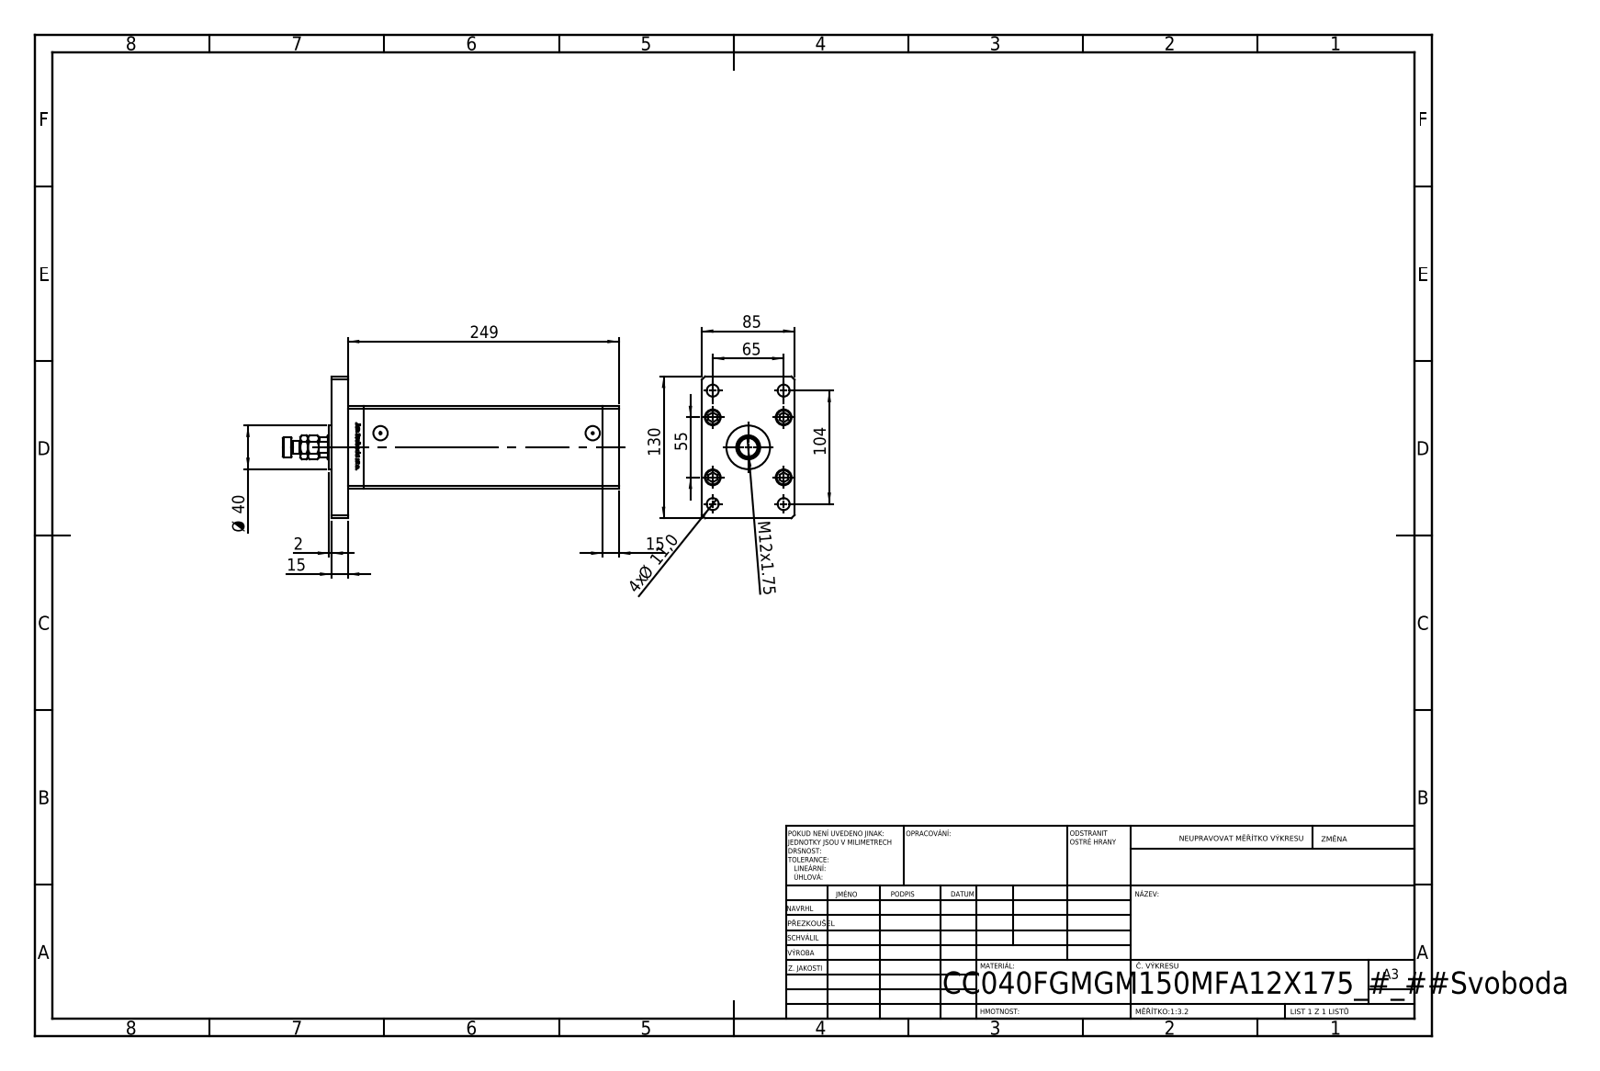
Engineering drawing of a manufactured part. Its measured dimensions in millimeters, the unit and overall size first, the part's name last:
Units: millimetres
Overall size (bounding box): 308 × 130 × 85
Round holes (diameter × count): ⌀11 ×9, ⌀15.5 ×5, ⌀10 ×4, ⌀14.5 ×4, ⌀2 ×2, ⌀13.16 ×2, ⌀13.5 ×1, ⌀22 ×1, ⌀23.5 ×1
Round bosses / shafts (diameter × count): ⌀8 ×9, ⌀14.5 ×5, ⌀40 ×1, ⌀18 ×1, ⌀11 ×1
Partial cylindrical surfaces — rounded edges, fillets, slot ends (radius × count): R0.93 ×2, R10.5 ×1
Main face-to-face distances: 15, 85, 75, 233.5, 248.5, 218.5, 30, 263.5, 10.5, 27.5
Hole centre spacings: 28, 24.5, 42.57, 61.32, 65, 69.46, 79.5, 102.69
Volume: 1 544 000 mm³ · Surface area: 238 953 mm²
Bodies: 20 solids, 1360 faces (531 planar, 191 cylindrical, 638 other)
Part name (STEP PRODUCT): V220C_VC_F; V220C_F_MIDDLE; ALLEN BOLT; MFA (+3 more)
STEP written by: SolidWorks 2019 (CONFIG_CONTROL_DESIGN)
